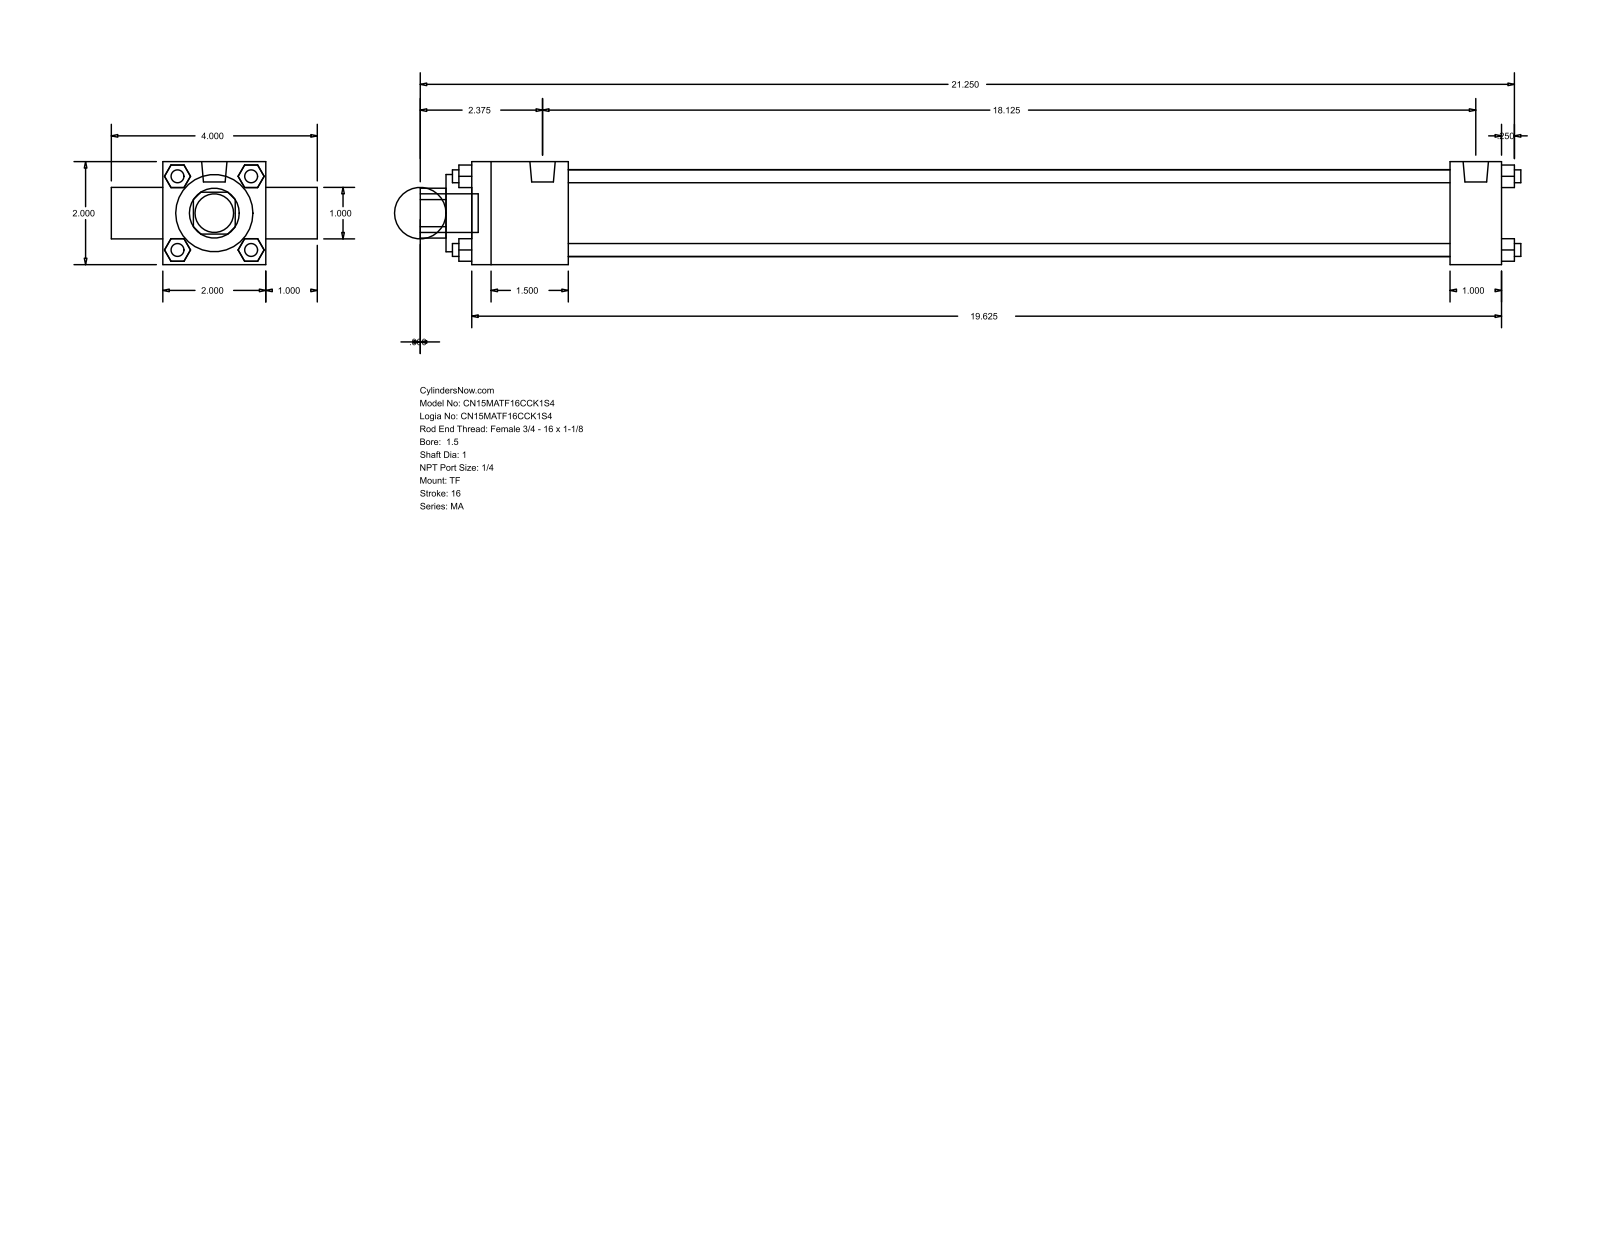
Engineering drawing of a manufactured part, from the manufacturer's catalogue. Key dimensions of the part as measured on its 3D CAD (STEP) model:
Part name (STEP PRODUCT): MA_TF__0150_1
STEP written by: GSSL Pune (CONFIG_CONTROL_DESIGN)
Units: millimetres
Bodies: 0 solids, 120 faces (92 planar, 28 cylindrical, 0 other)
Overall size (bounding box): 542.92 × 101.6 × 50.8
Round holes (diameter × count): ⌀25.4 ×2, ⌀38.1 ×1, ⌀42.93 ×1
Round bosses / shafts (diameter × count): ⌀6.35 ×4, ⌀7.94 ×3, ⌀12.49 ×2, ⌀19.05 ×1
Partial cylindrical surfaces — rounded edges, fillets, slot ends (radius × count): R12.29 ×1
Main face-to-face distances: 50.8, 25.4, 508, 76.2, 6.35, 47.63, 482.6, 434.97, 460.37, 520.7
